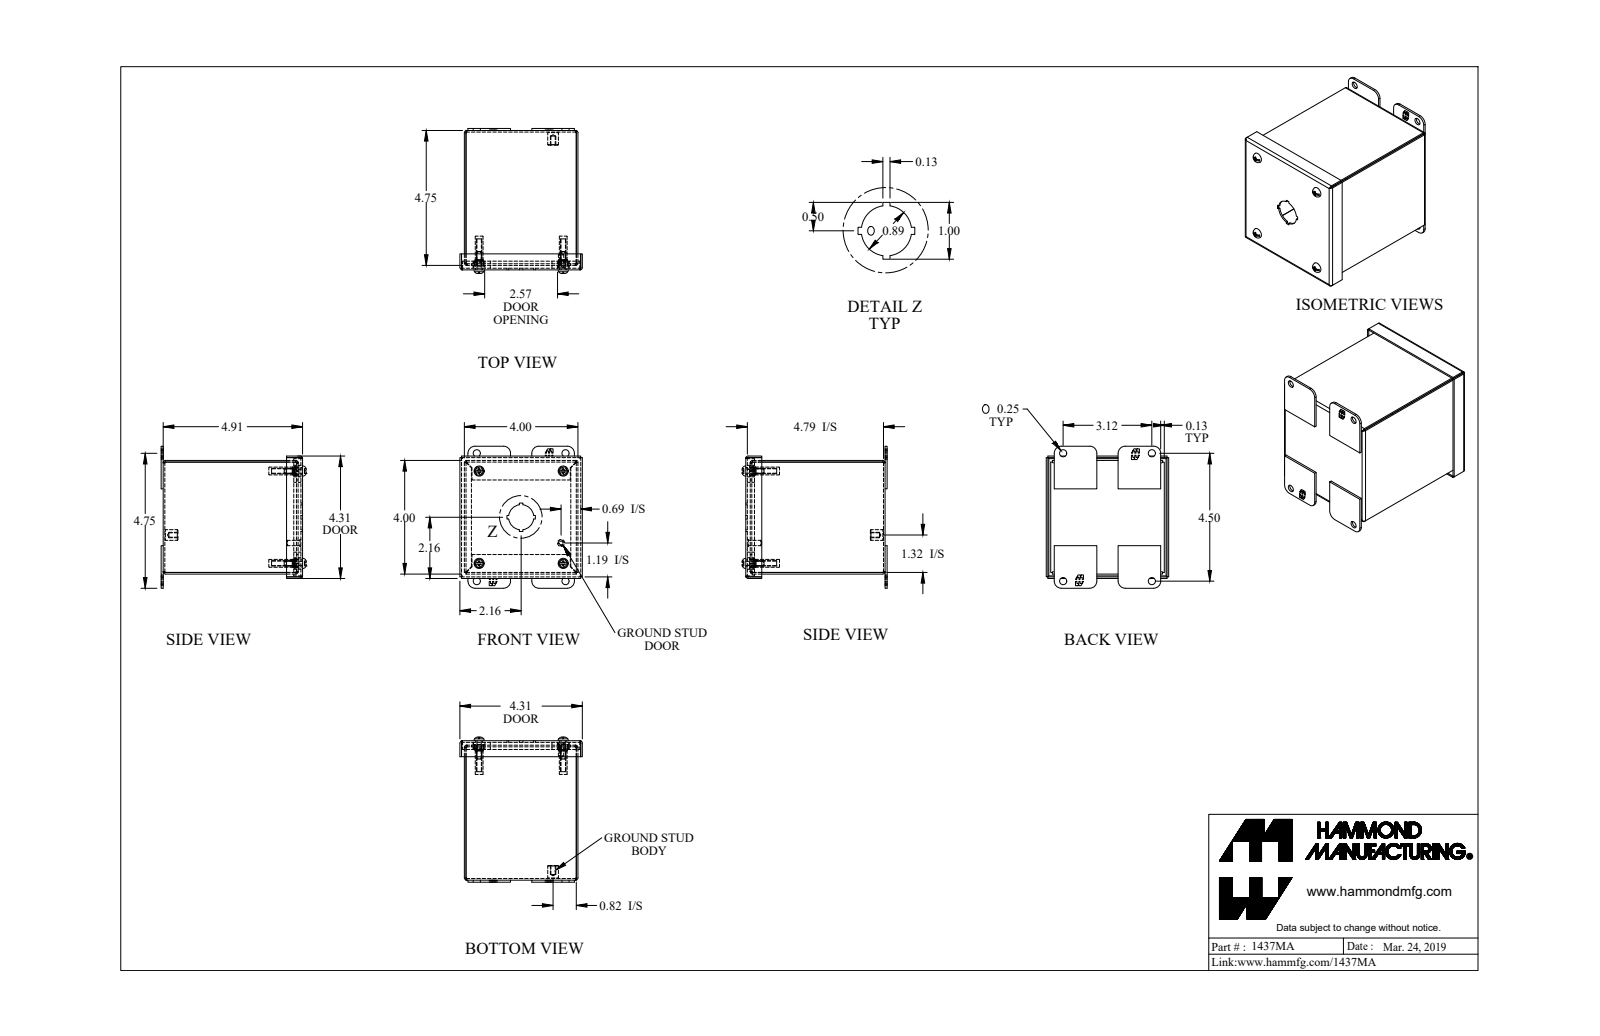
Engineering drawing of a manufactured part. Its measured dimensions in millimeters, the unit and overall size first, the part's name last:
Units: millimetres
Overall size (bounding box): 129.7 × 127 × 109.5
Round holes (diameter × count): ⌀6.4 ×8, ⌀4 ×4, ⌀10.3 ×4, ⌀4 ×1, ⌀22.5 ×1
Round bosses / shafts (diameter × count): ⌀9.9 ×4, ⌀7 ×4, ⌀4.8 ×4, ⌀3.8 ×4, ⌀9.5 ×1, ⌀6.4 ×1, ⌀4.8 ×1
Partial cylindrical surfaces — rounded edges, fillets, slot ends (radius × count): R0.7 ×12, R2.2 ×12, R6.4 ×8, R4.1 ×4, R4.3 ×4
Main face-to-face distances: 1.4, 100.2, 123.2, 101.6, 98.7, 124.6, 4, 104.1, 121.7, 4
Hole centre spacings: 82.6, 78.9, 111.7, 111.7, 16, 69.6, 75.2, 78.9
Volume: 152 600 mm³ · Surface area: 190 900 mm²
Bodies: 21 solids, 651 faces (447 planar, 148 cylindrical, 56 other)
Part name (STEP PRODUCT): 1437MA_Default
STEP written by: SolidWorks 2019 (CONFIG_CONTROL_DESIGN)
